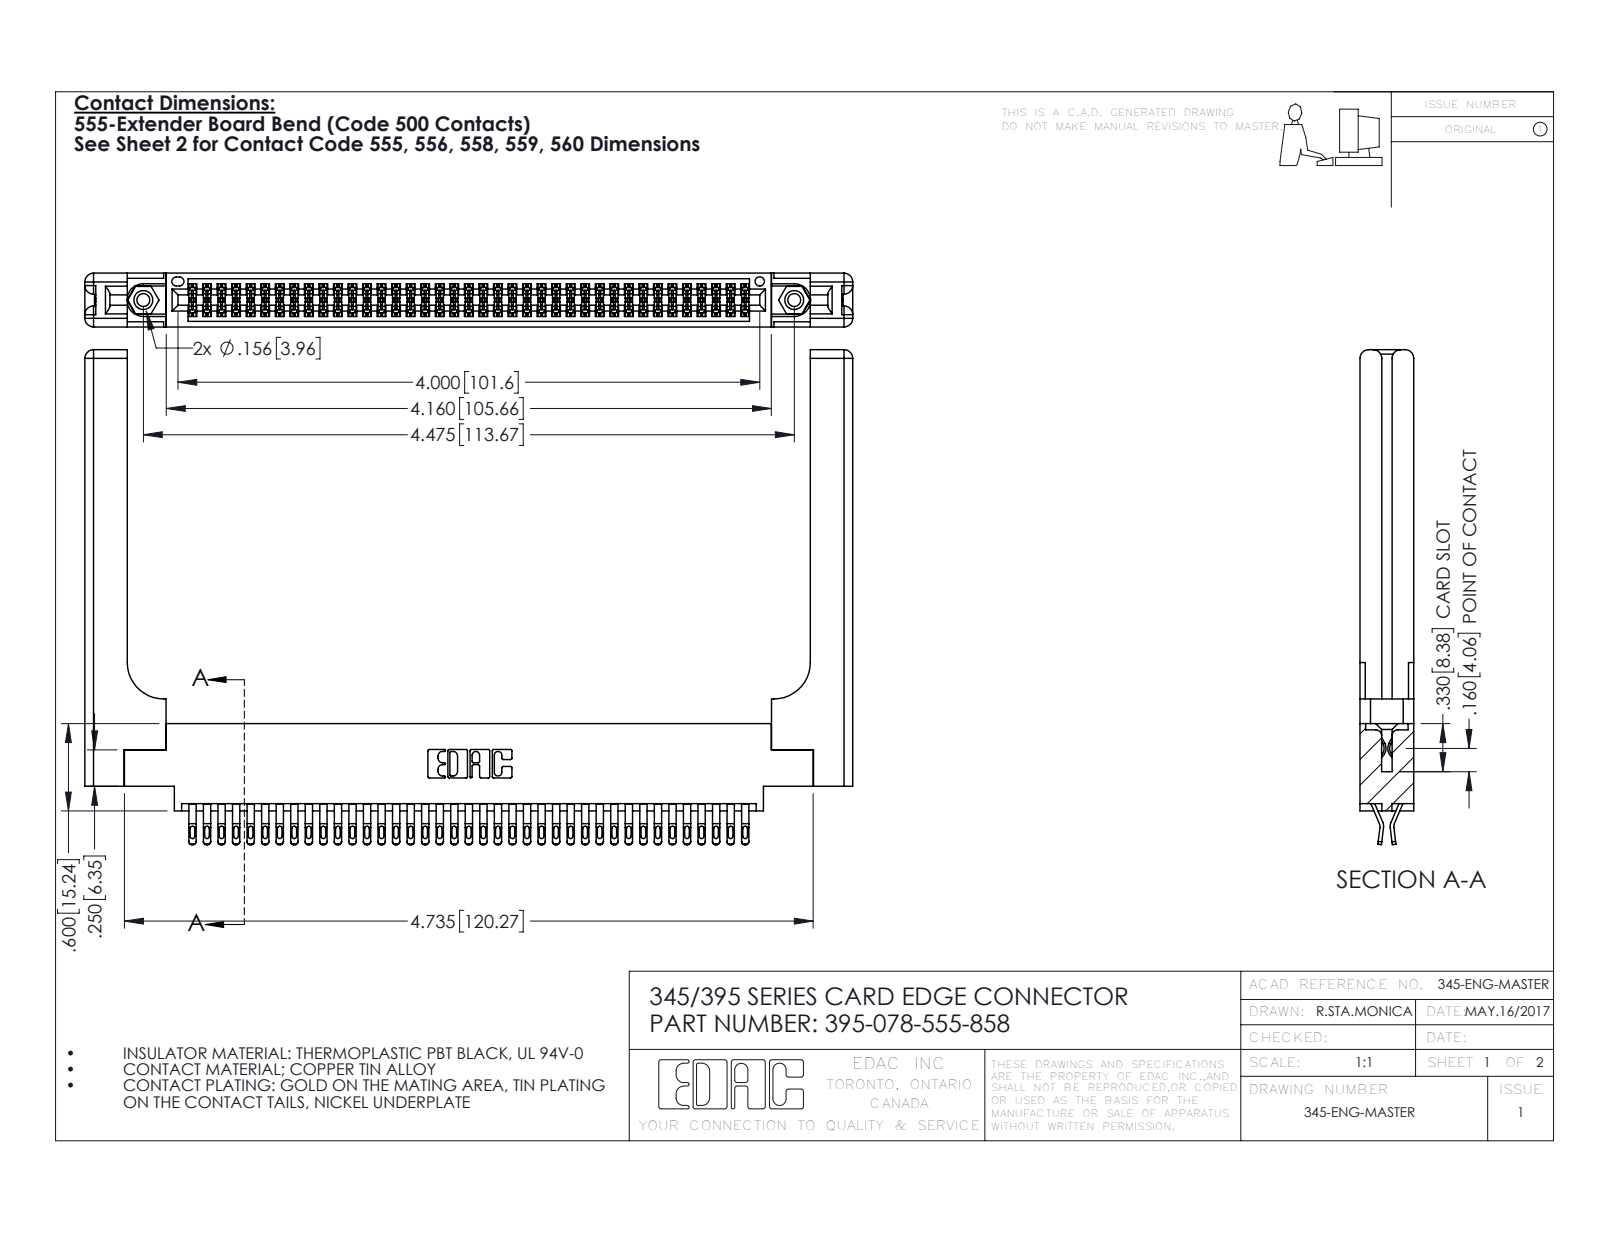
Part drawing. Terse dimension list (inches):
name: 395-078-555-858; 345-250-001_345-250-001-102; 345 Part_0.170 Offset - 0.156 Dia-TH; 345-292-001_555 Tail (+1 more)
written by: SolidWorks 2016 (CONFIG_CONTROL_DESIGN)
unit: in
bodies: 83 solids, 4754 faces (2650 planar, 2044 cylindrical, 60 other)
size: 5.279 × 3.402 × 0.37
volume: 1.317 in³; area: 39.23 in²
holes: 2× ⌀0.089, 2× ⌀0.125, 2× ⌀0.156, 1× ⌀0.064
bosses: 2× ⌀0.155
rounds: 195× R0.016, 156× R0.02, 117× R0.006, 22× R0.01, 16× R0.06, 6× R0.007, 6× R0.031, 3× R0.026
face distances: 0.37, 0.072, 0.298, 0.025, 0.098, 0.272, 0.2, 0.225, 0.148, 0.15
hole spacings: 0.27, 4.239, 4.475
